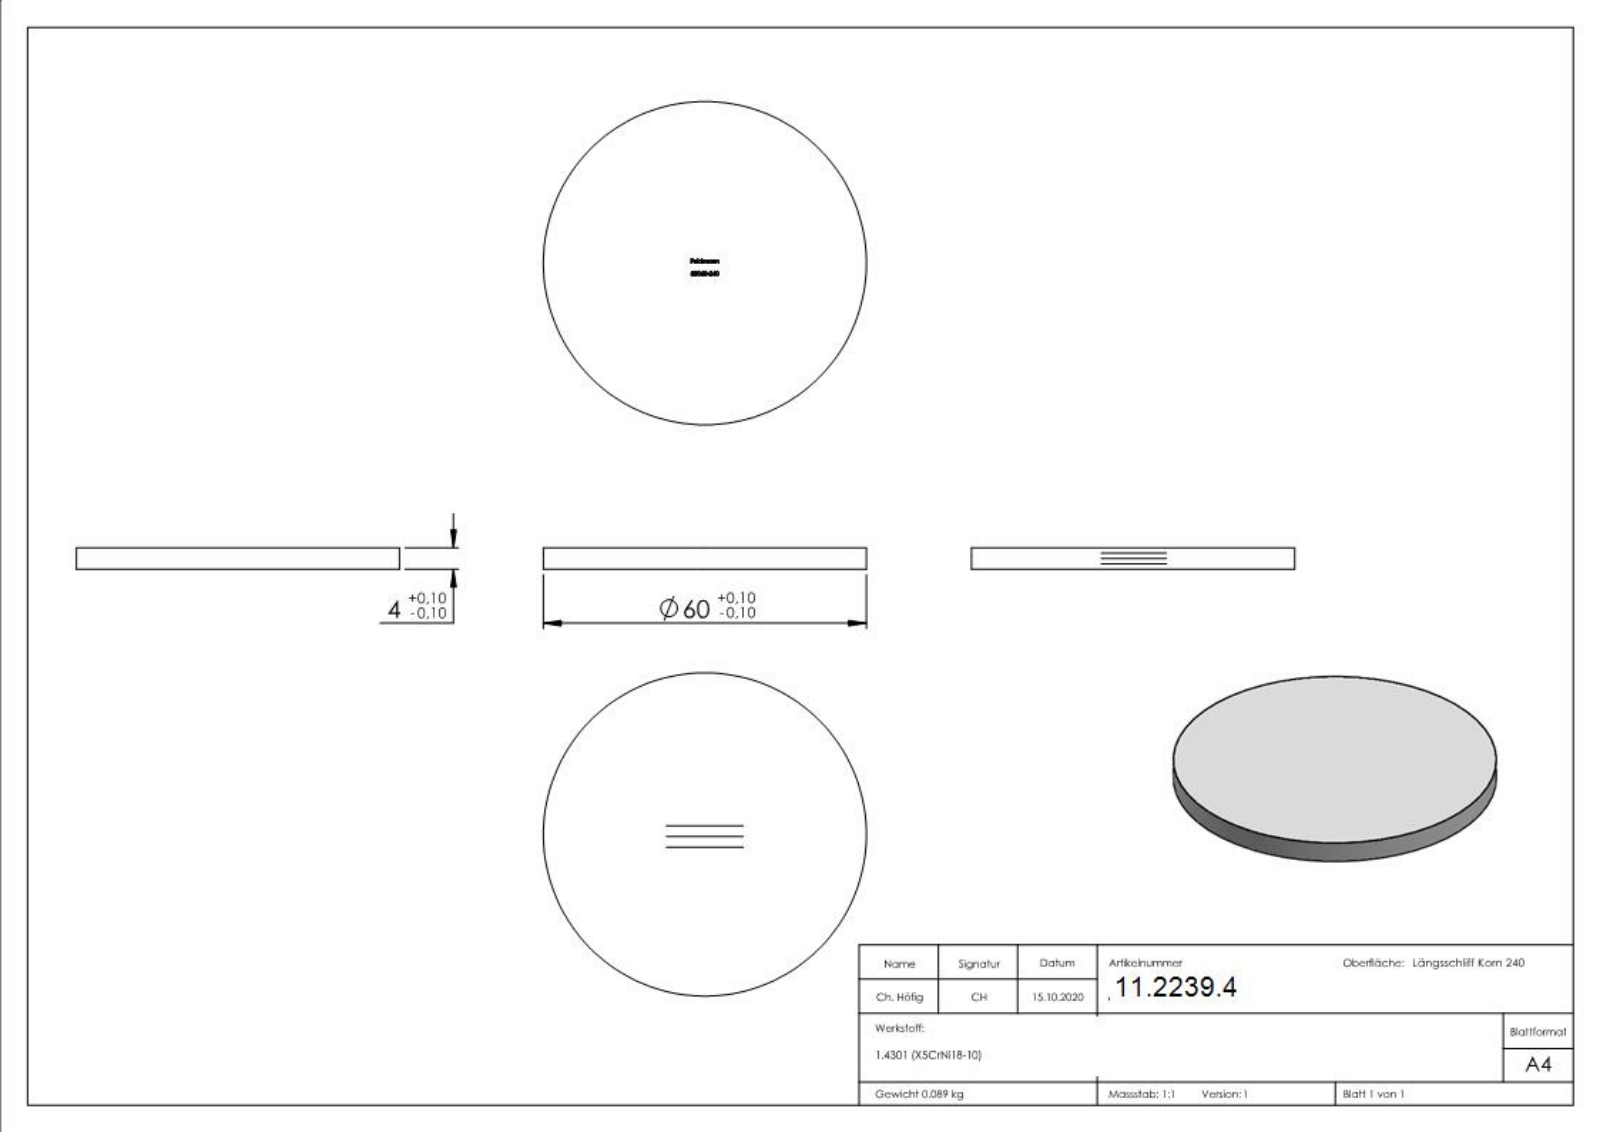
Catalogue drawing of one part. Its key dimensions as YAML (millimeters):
part_name: "53060-240"
step_written_by: "SolidWorks 2018 (CONFIG_CONTROL_DESIGN)"
units: millimeters
bodies: {solids: 1, faces: 230, planar: 116, cylindrical: 2, other: 112}
overall_size: [60, 60, 4]
volume: 11310
surface_area: 6415
round_bosses_or_shafts:
  - {diameter: 60, count: 1}
face_to_face_distances: [4, 3.9, 1.78, 2.45, 0.83, 2.41, 0.99, 0.4, 2.77, 0.67]
